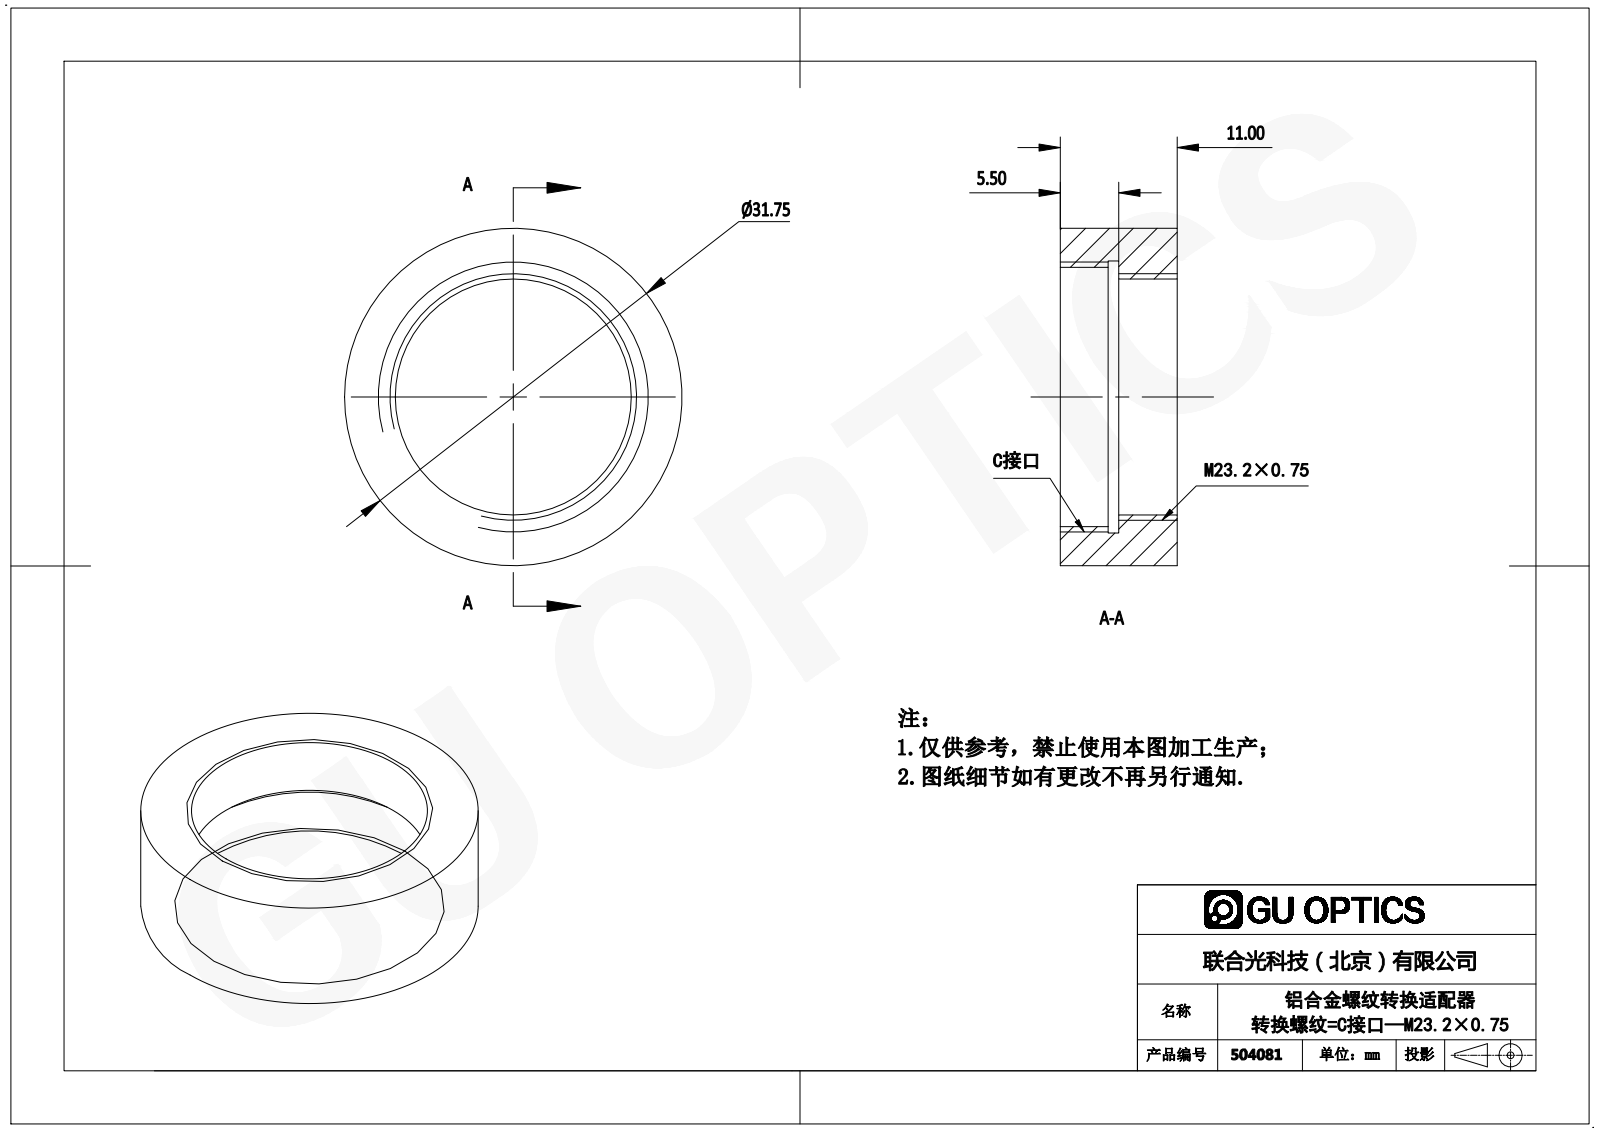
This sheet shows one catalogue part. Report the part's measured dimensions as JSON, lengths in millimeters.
{"part_name": "504081", "step_written_by": "SolidWorks 2016 (AUTOMOTIVE_DESIGN)", "units": "millimeters", "bodies": {"solids": 1, "faces": 12, "planar": 4, "cylindrical": 8, "other": 0}, "overall_size": [31.75, 31.75, 11], "volume_mm3": 3961, "surface_area_mm2": 2810, "round_holes": [[22.2, 1], [24.4, 1], [25.6, 1]], "round_bosses_or_shafts": [[31.75, 1]], "face_to_face_distances": [11, 5.5, 4.5, 1, 6.5]}
